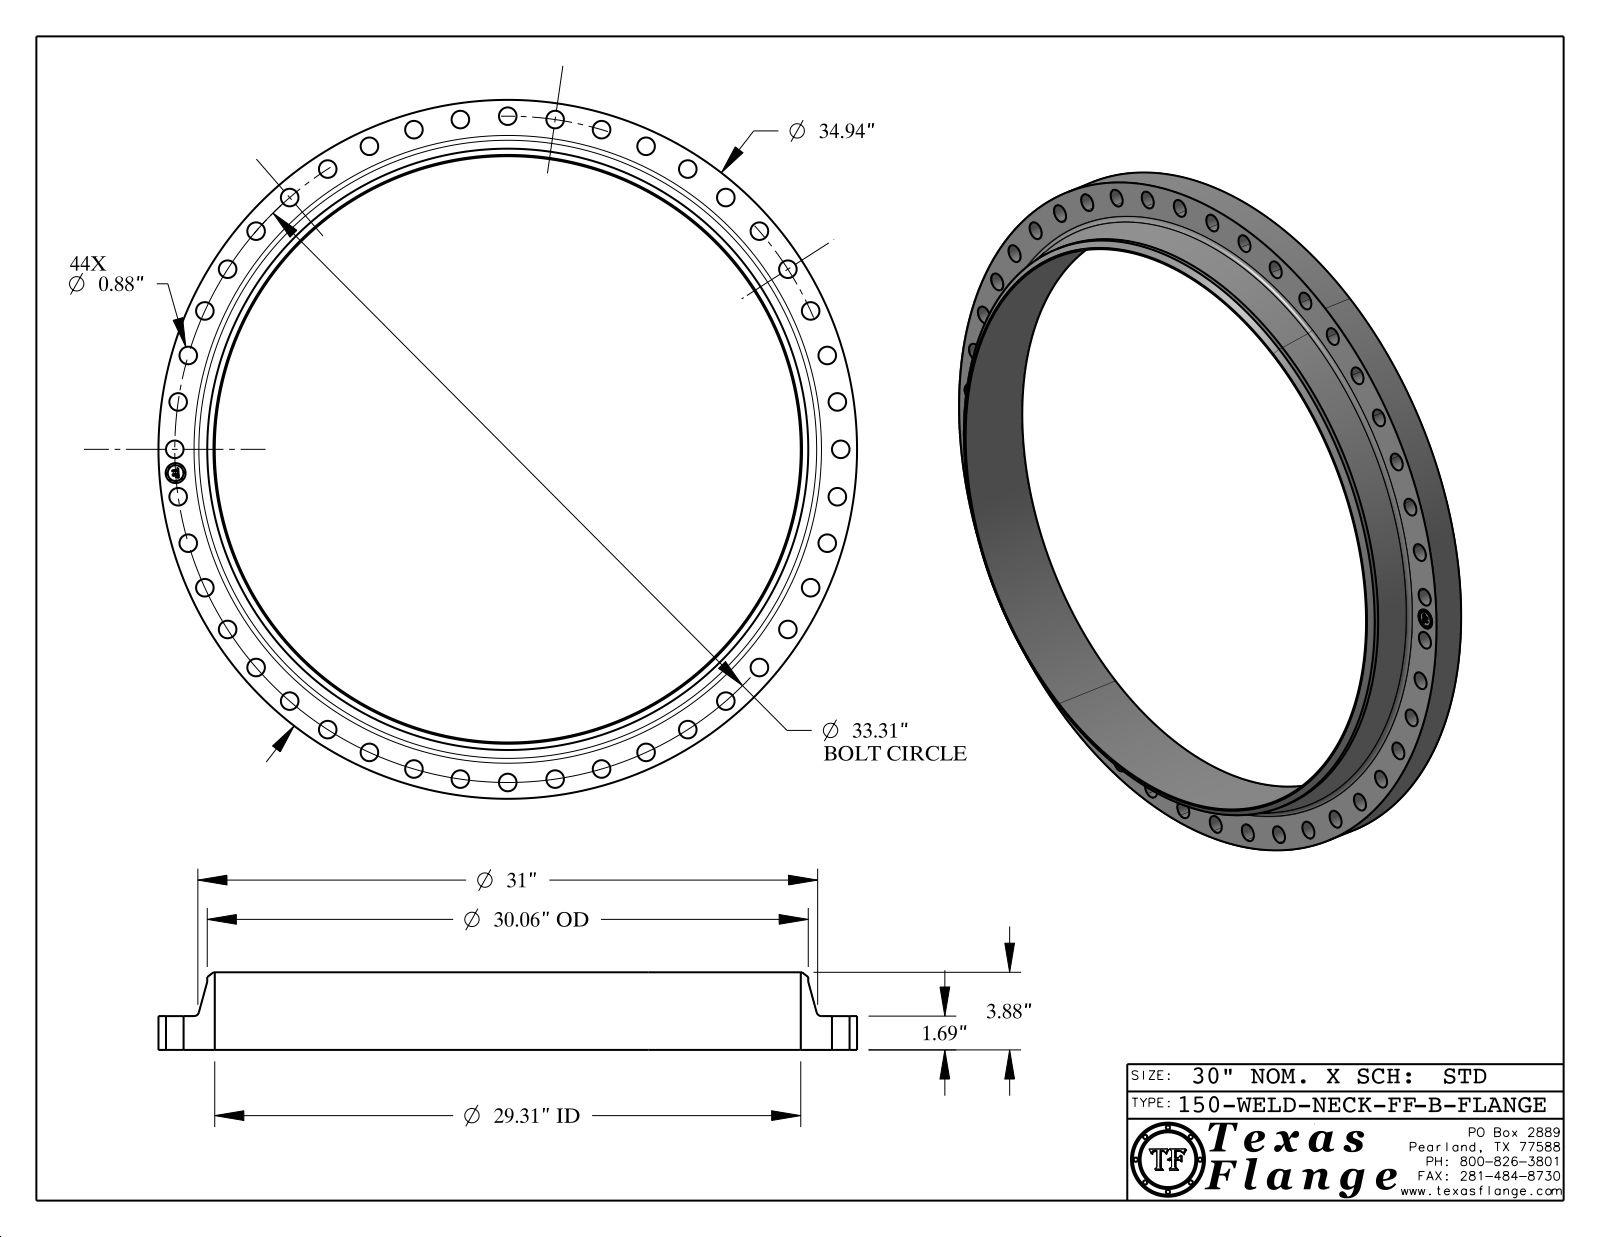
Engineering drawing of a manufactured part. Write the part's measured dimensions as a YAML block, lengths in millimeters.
part_name: "150-WELD-NECK-FF, Series B"
step_written_by: "CATIA V5 STEP AP214 (AUTOMOTIVE_DESIGN)"
units: millimeters
bodies: {solids: 1, faces: 488, planar: 368, cylindrical: 114, other: 6}
overall_size: [887.5, 887.5, 98.6]
volume: 8965000
surface_area: 911600
round_holes:
  - {diameter: 22.4, count: 44}
  - {diameter: 25.4, count: 1}
  - {diameter: 744.5, count: 1}
round_bosses_or_shafts:
  - {diameter: 1.5, count: 8}
  - {diameter: 887.5, count: 1}
  - {diameter: 763.5, count: 1}
  - {diameter: 20, count: 1}
face_to_face_distances: [42.9, 98.6, 55.6, 0.4, 42.5, 56, 7.6, 7.4, 1.4, 4.9]
hole_center_spacings: [423, 60.4, 843.9, 811.8, 837.5, 826.7, 120.4, 295.7]
